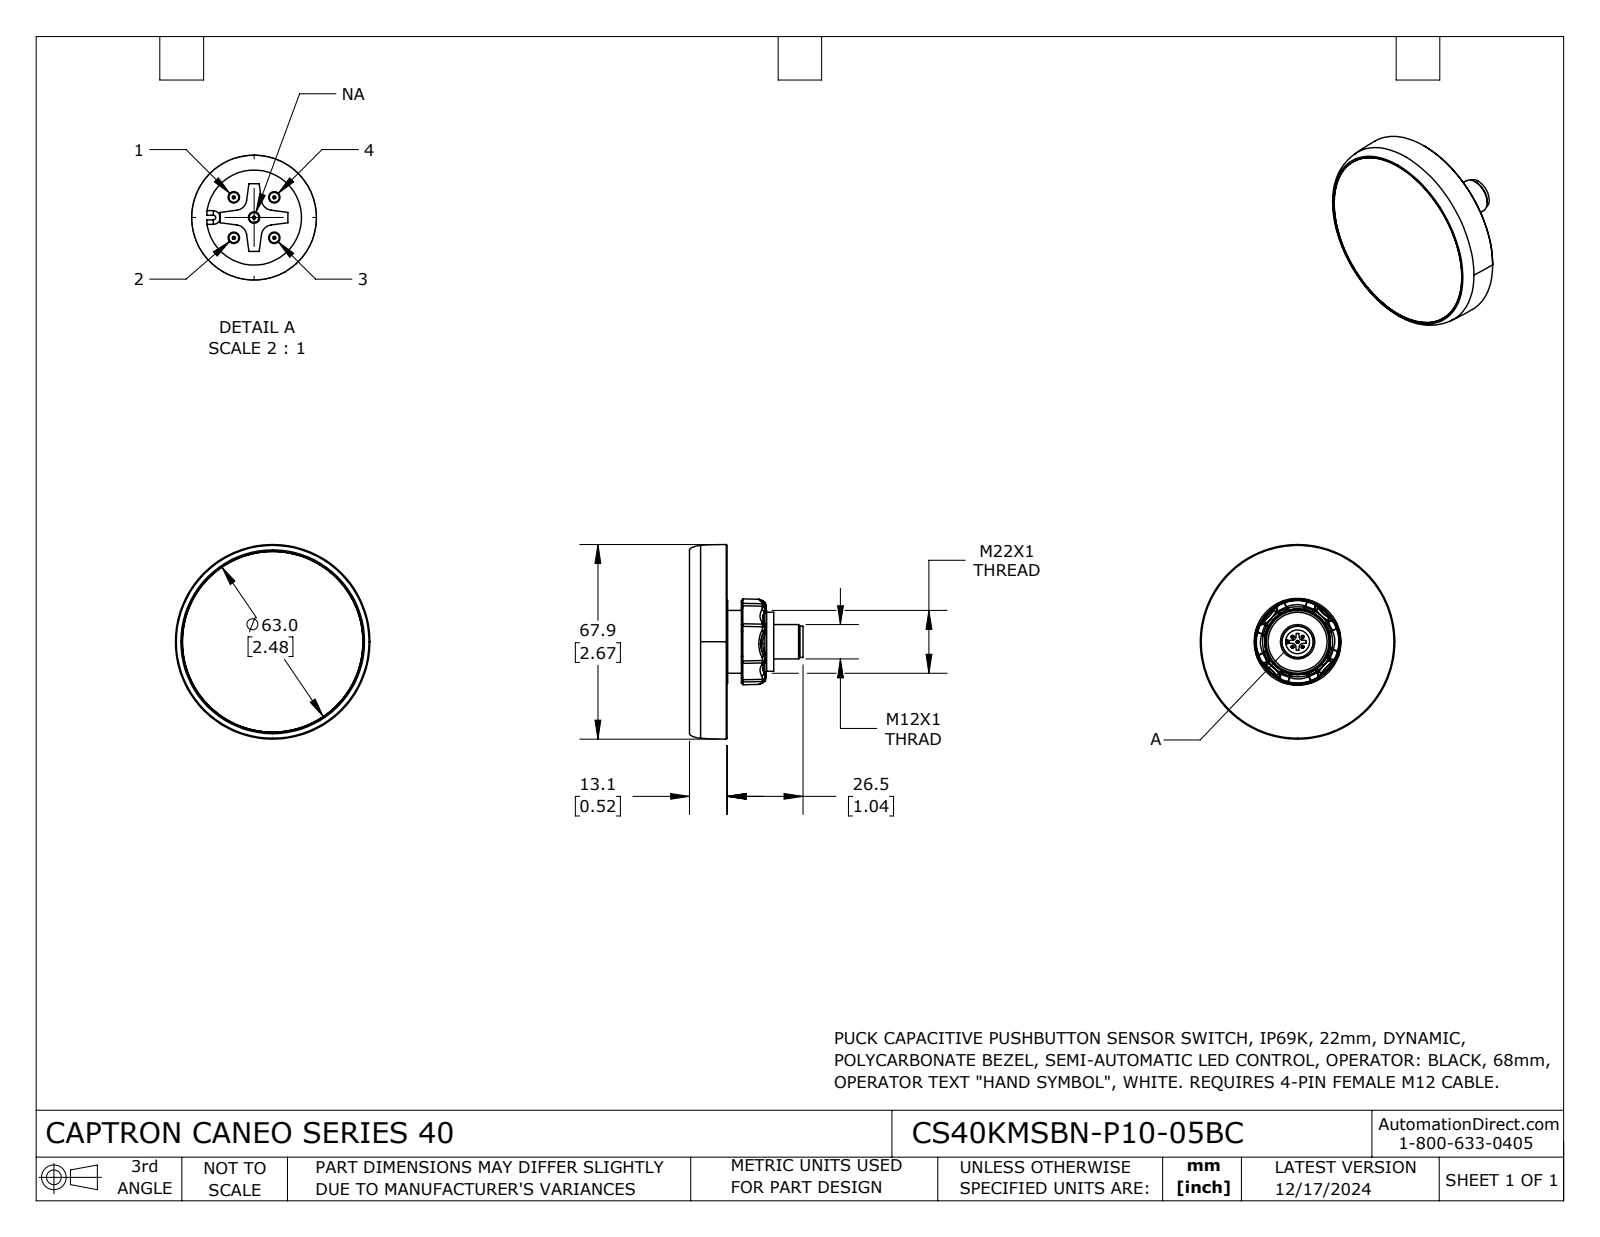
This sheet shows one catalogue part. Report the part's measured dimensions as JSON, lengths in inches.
{"part_name": "CS40KMSBN-P10-05BC", "step_written_by": "SolidWorks 2024 (CONFIG_CONTROL_DESIGN)", "units": "inches", "bodies": {"solids": 3, "faces": 420, "planar": 62, "cylindrical": 50, "other": 308}, "overall_size": [2.673, 2.673, 1.559], "volume_in3": 3.397, "surface_area_in2": 23.2, "round_holes": [[0.327, 1], [0.827, 1], [0.927, 1], [1.193, 1], [2.484, 1]], "round_bosses_or_shafts": [[0.039, 5], [2.48, 1], [0.862, 1], [0.811, 1], [0.472, 1], [0.429, 1]], "partial_cylinders_radius": [[0.295, 8], [0.039, 4], [0.689, 4], [0.016, 2], [0.024, 1]], "face_to_face_distances": [0.516, 0.02, 0.496, 0.642, 0.661, 1.157, 0.217, 0.713, 0.197, 0.659]}
